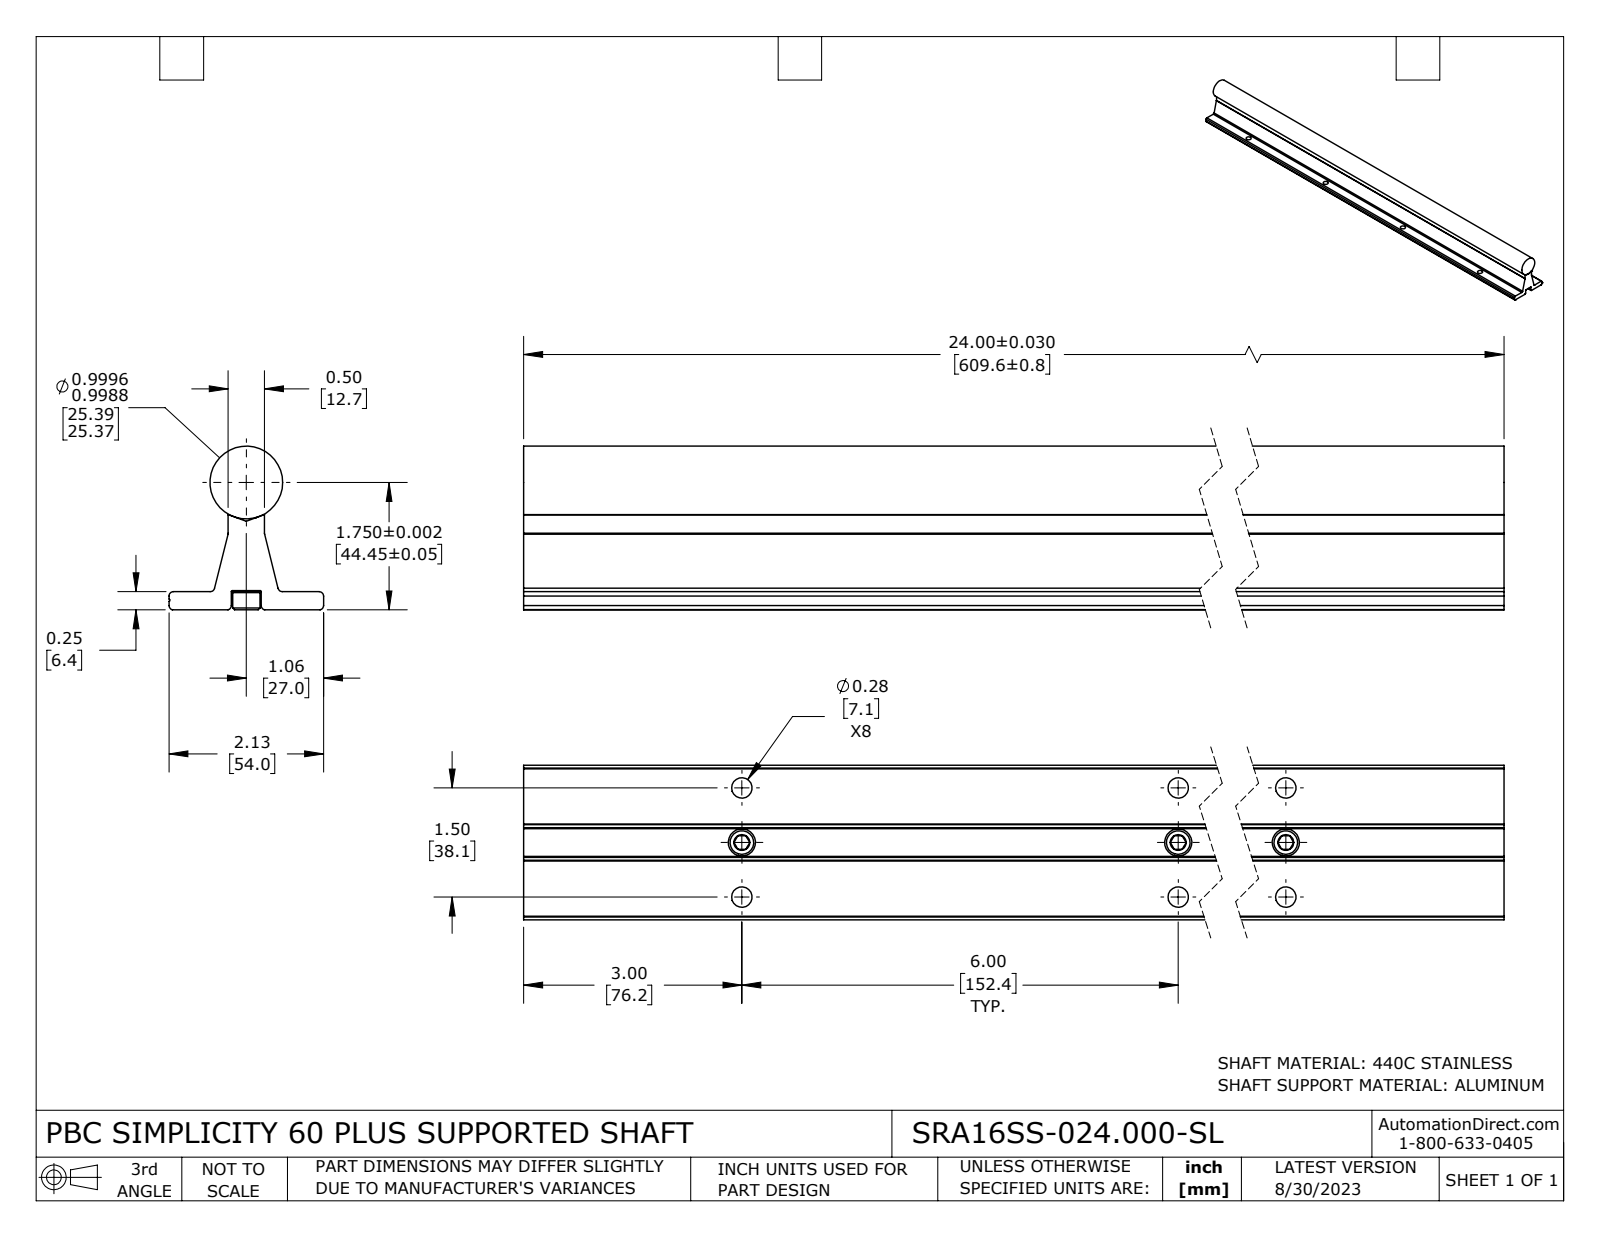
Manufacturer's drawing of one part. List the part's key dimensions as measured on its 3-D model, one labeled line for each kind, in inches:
Part name (STEP PRODUCT): SRA16SS-024.000-SL
STEP written by: SolidWorks 2021 (CONFIG_CONTROL_DESIGN)
Units: inches
Bodies: 6 solids, 203 faces (71 planar, 72 cylindrical, 60 other)
Overall size (bounding box): 24 × 2.25 × 2.125
Volume: 44.75 in³ · Surface area: 257.5 in²
Round holes (diameter × count): ⌀0.281 ×12, ⌀0.213 ×4, ⌀0.313 ×4
Round bosses / shafts (diameter × count): ⌀0.375 ×4, ⌀0.25 ×4, ⌀1 ×1
Partial cylindrical surfaces — rounded edges, fillets, slot ends (radius × count): R0.06 ×6, R0.063 ×4, R0.015 ×2, R0.032 ×2
Main face-to-face distances: 0.25, 0.045, 0.455, 0.265, 0.015, 0.5, 0.813, 0.857, 1.268, 1.313
Hole centre spacings: 6.047, 6, 0.75, 12.023, 6.185, 12, 1.5, 12.093
